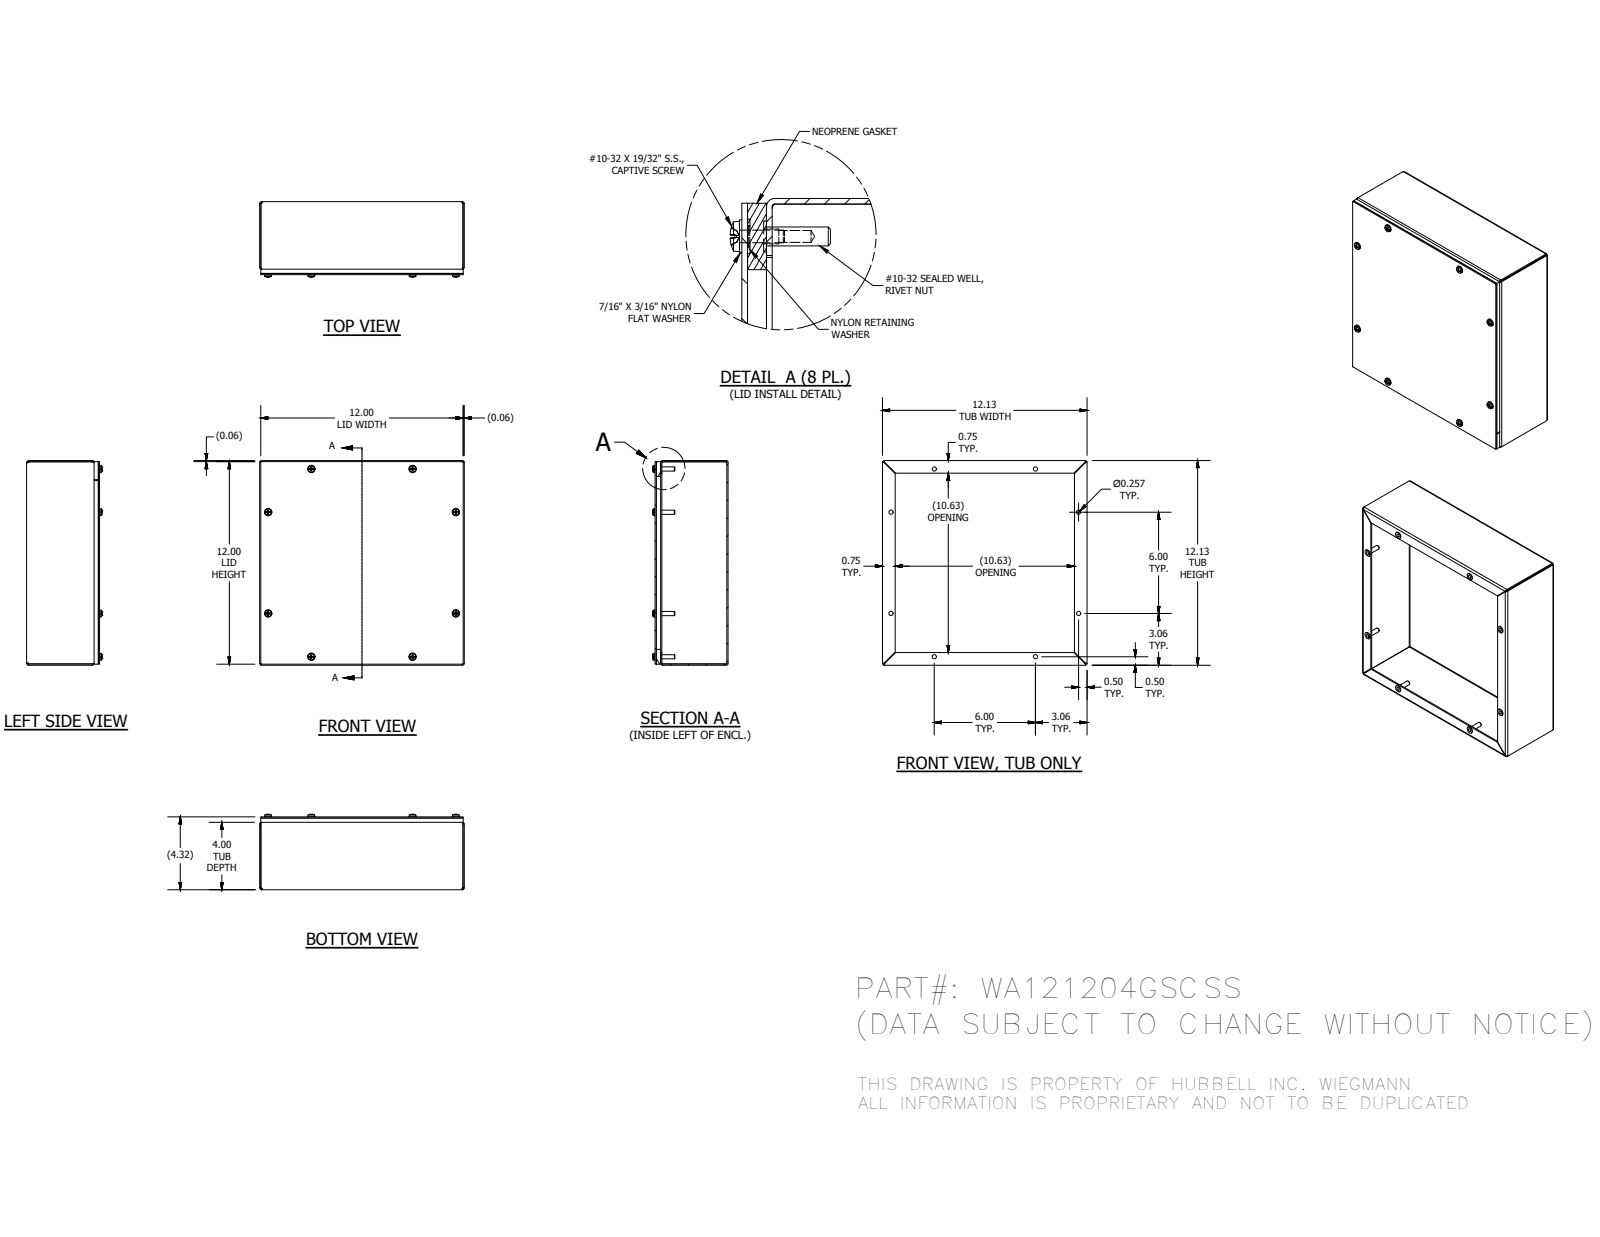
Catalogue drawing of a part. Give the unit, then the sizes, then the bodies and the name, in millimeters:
Units: millimetres
Overall size (bounding box): 307.98 × 307.98 × 113.75
Round holes (diameter × count): ⌀3.96 ×8, ⌀4.78 ×8, ⌀4.98 ×8, ⌀6.53 ×8, ⌀7.06 ×8, ⌀7.14 ×8, ⌀7.95 ×8
Round bosses / shafts (diameter × count): ⌀11.51 ×8, ⌀11.11 ×8, ⌀10.31 ×8, ⌀6.3 ×8, ⌀4.25 ×8
Partial cylindrical surfaces — rounded edges, fillets, slot ends (radius × count): R0.79 ×12, R1.78 ×8, R2.27 ×8, R2.67 ×8
Main face-to-face distances: 1.88, 107.95, 306.1, 109.83, 106.07, 99.72, 8.23, 307.98, 304.22, 6.35
Hole centre spacings: 152.4, 227, 227.02, 92.04, 282.56, 307.56, 321.04, 92.02
Volume: 778 833 mm³ · Surface area: 738 996 mm²
Bodies: 36 solids, 764 faces (420 planar, 160 cylindrical, 184 other)
Part name (STEP PRODUCT): WA121204GSCSSBKP; WA1212GSCSSLID; 316282; 37210 (+4 more)
STEP written by: Autodesk Inventor 2016 (AUTOMOTIVE_DESIGN)
